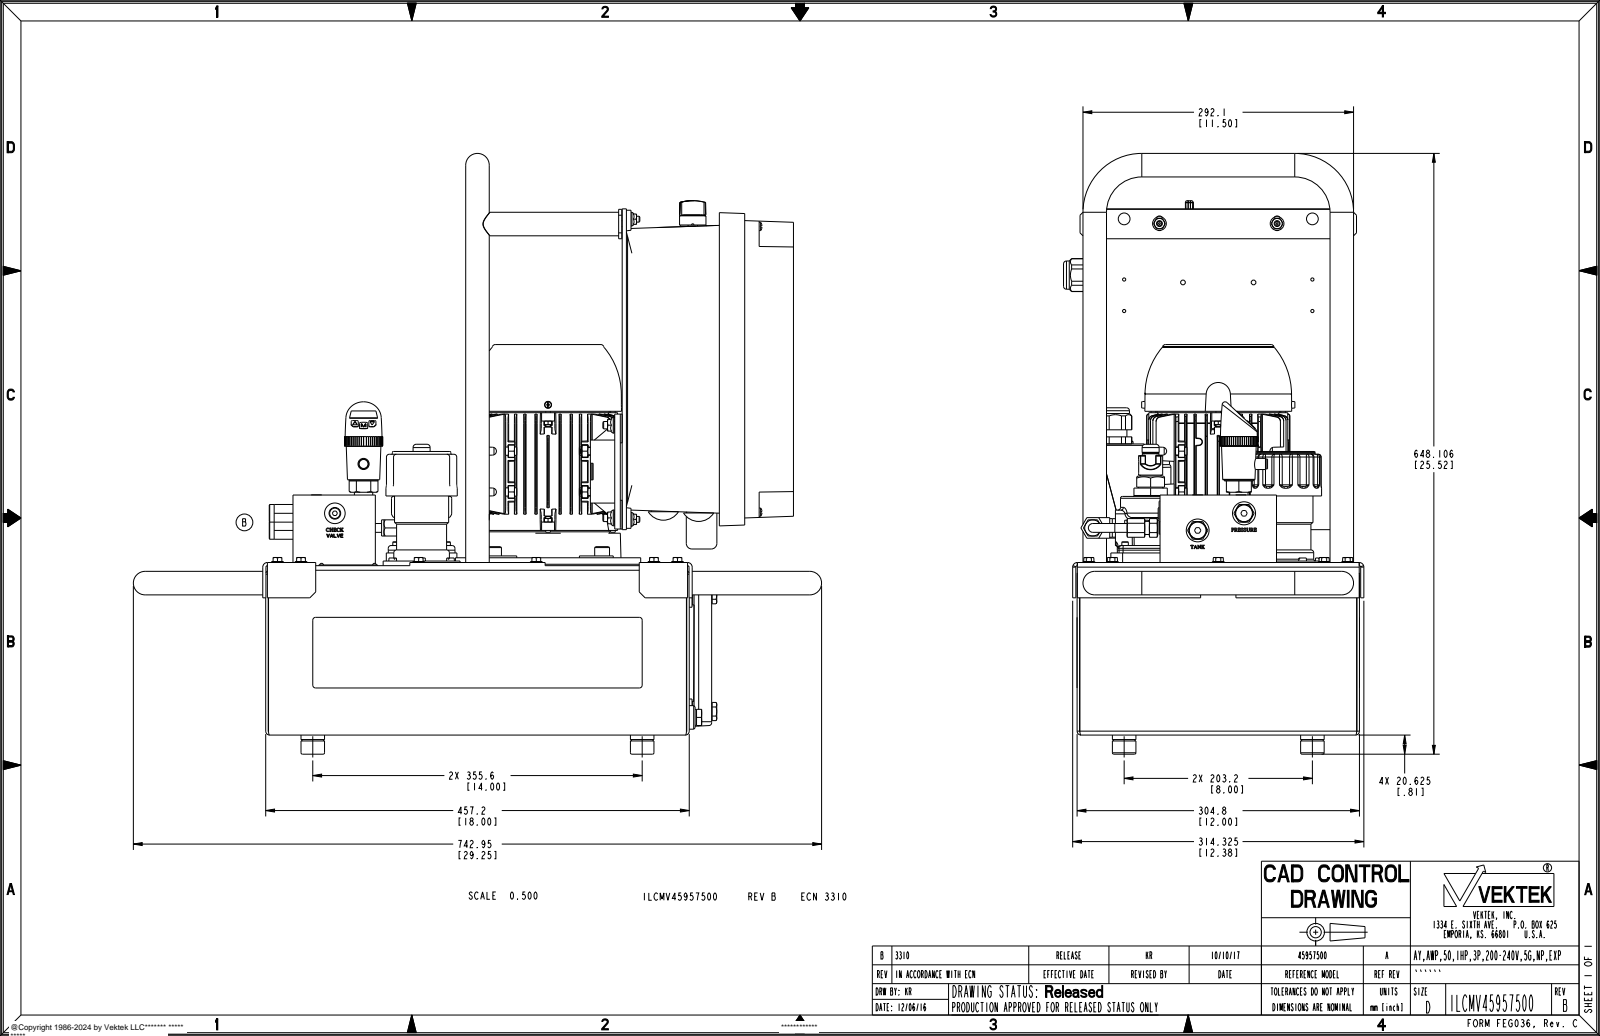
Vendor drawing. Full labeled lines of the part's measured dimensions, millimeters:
Part name (STEP PRODUCT): ILCMV45957500
STEP written by: PRO/ENGINEER BY PARAMETRIC TECHNOLOGY CORPORATION, 2013320 (AUTOMOTIVE_DESIGN)
Units: millimetres
Bodies: 20 solids, 10008 faces (4898 planar, 2411 cylindrical, 2699 other)
Overall size (bounding box): 742.95 × 648.11 × 324.21
Volume: 10 620 000 mm³ · Surface area: 3 320 000 mm²
Round holes (diameter × count): ⌀7.92 ×14, ⌀8.74 ×14, ⌀9.53 ×14, ⌀3.45 ×13, ⌀6 ×11, ⌀19.05 ×9, ⌀3 ×8, ⌀11.99 ×8, ⌀5.51 ×6, ⌀5.54 ×6, ⌀5.99 ×6, ⌀8.99 ×6
Round bosses / shafts (diameter × count): ⌀6.35 ×24, ⌀25.4 ×14, ⌀12.7 ×14, ⌀5 ×14, ⌀9.53 ×9, ⌀8.89 ×8, ⌀4.5 ×8, ⌀14.83 ×6
Partial cylindrical surfaces — rounded edges, fillets, slot ends (radius × count): R0.5 ×82, R2 ×61, R0.13 ×54, R1 ×53, R3 ×42, R4 ×28, R2.75 ×18, R1.52 ×14
Main face-to-face distances: 2.66, 3.5, 302.13, 454.53, 184.9, 179.32, 176.66, 2.74, 182.16, 299.47
Hole centre spacings: 2.5, 203.2, 3.54, 14.38, 59.49, 70, 82.49, 98.99
